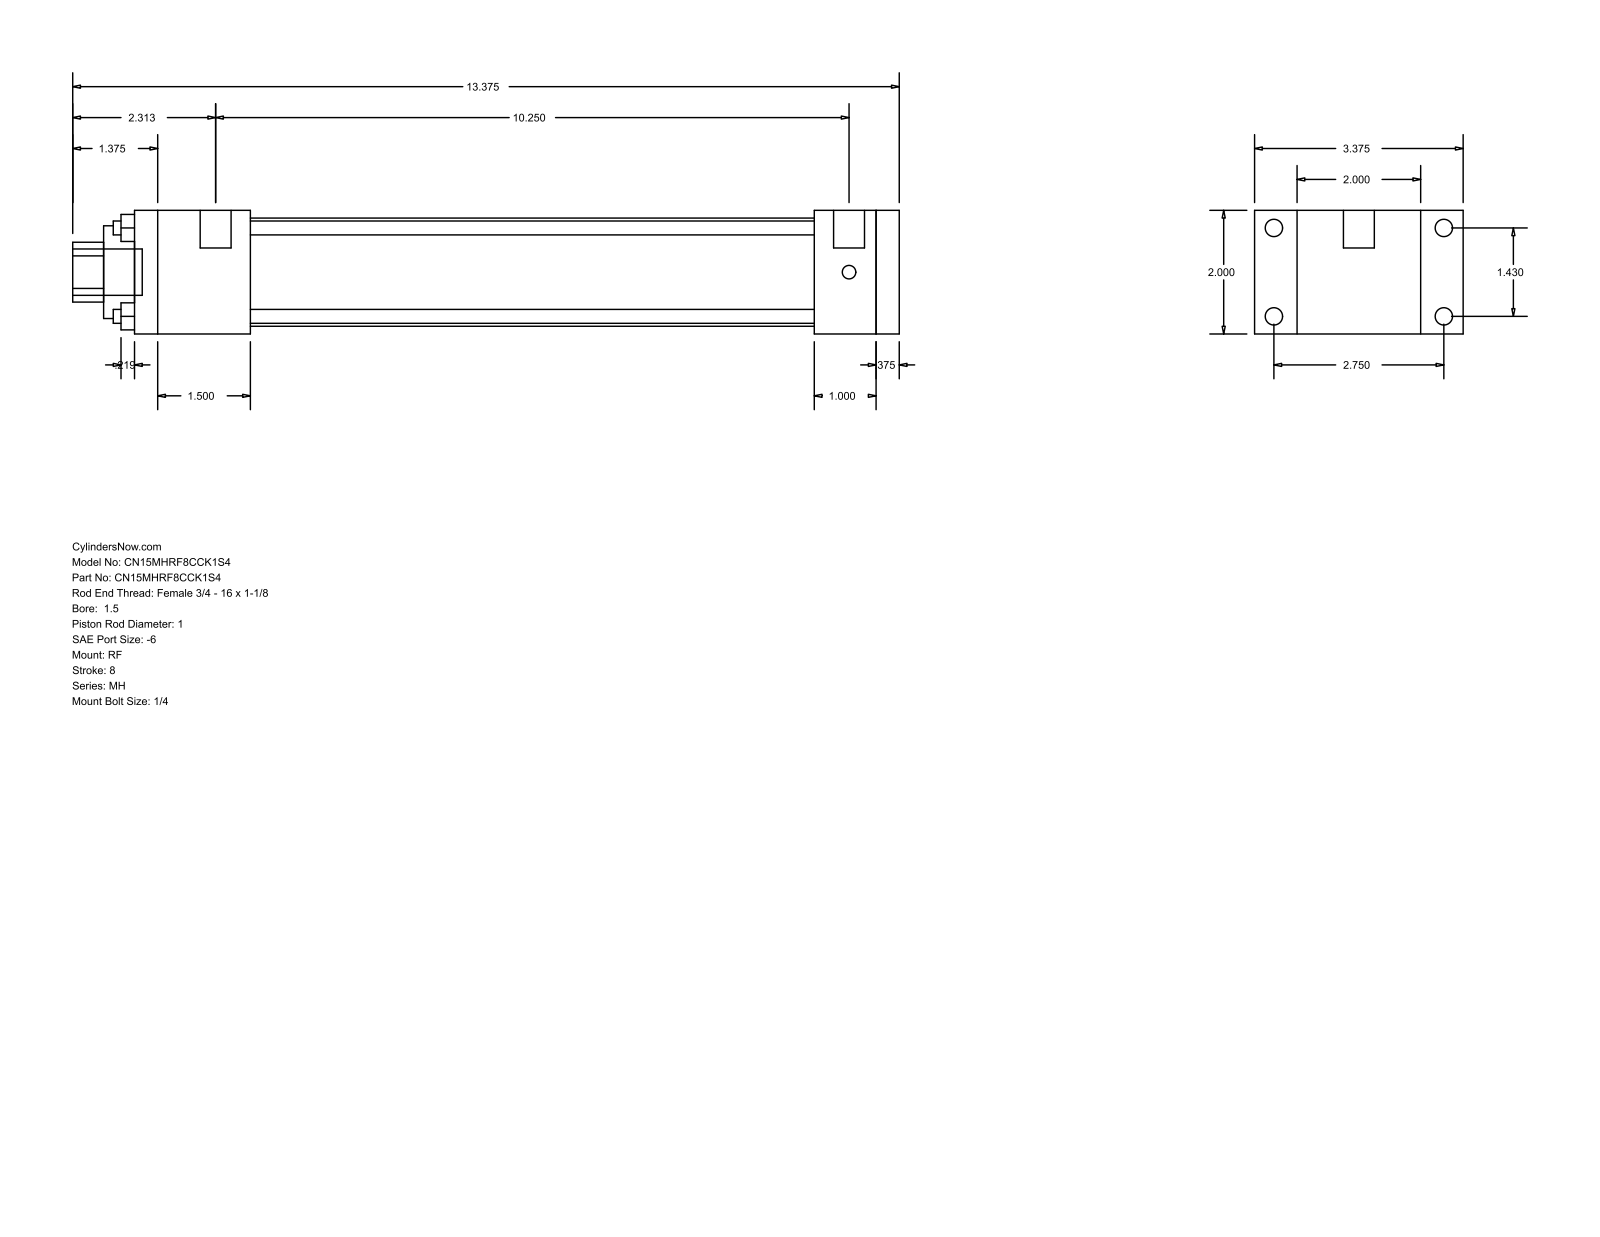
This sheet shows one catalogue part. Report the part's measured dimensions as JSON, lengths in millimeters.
{"part_name": "MH_RF__0150_1", "step_written_by": "GSSL Pune (CONFIG_CONTROL_DESIGN)", "units": "millimeters", "bodies": {"solids": 0, "faces": 92, "planar": 64, "cylindrical": 28, "other": 0}, "overall_size": [339.73, 85.72, 50.8], "round_holes": [[5.71, 4], [25.4, 1], [38.1, 1], [44.45, 1]], "round_bosses_or_shafts": [[7.14, 4], [5.56, 4], [12.7, 2], [19.05, 1]], "partial_cylinders_radius": [[12.29, 1]], "face_to_face_distances": [50.8, 9.53, 304.8, 25.4, 314.33, 17.46, 68.26, 279.4, 34.93, 47.63], "hole_center_spacings": [25.68, 36.32, 51.36]}
